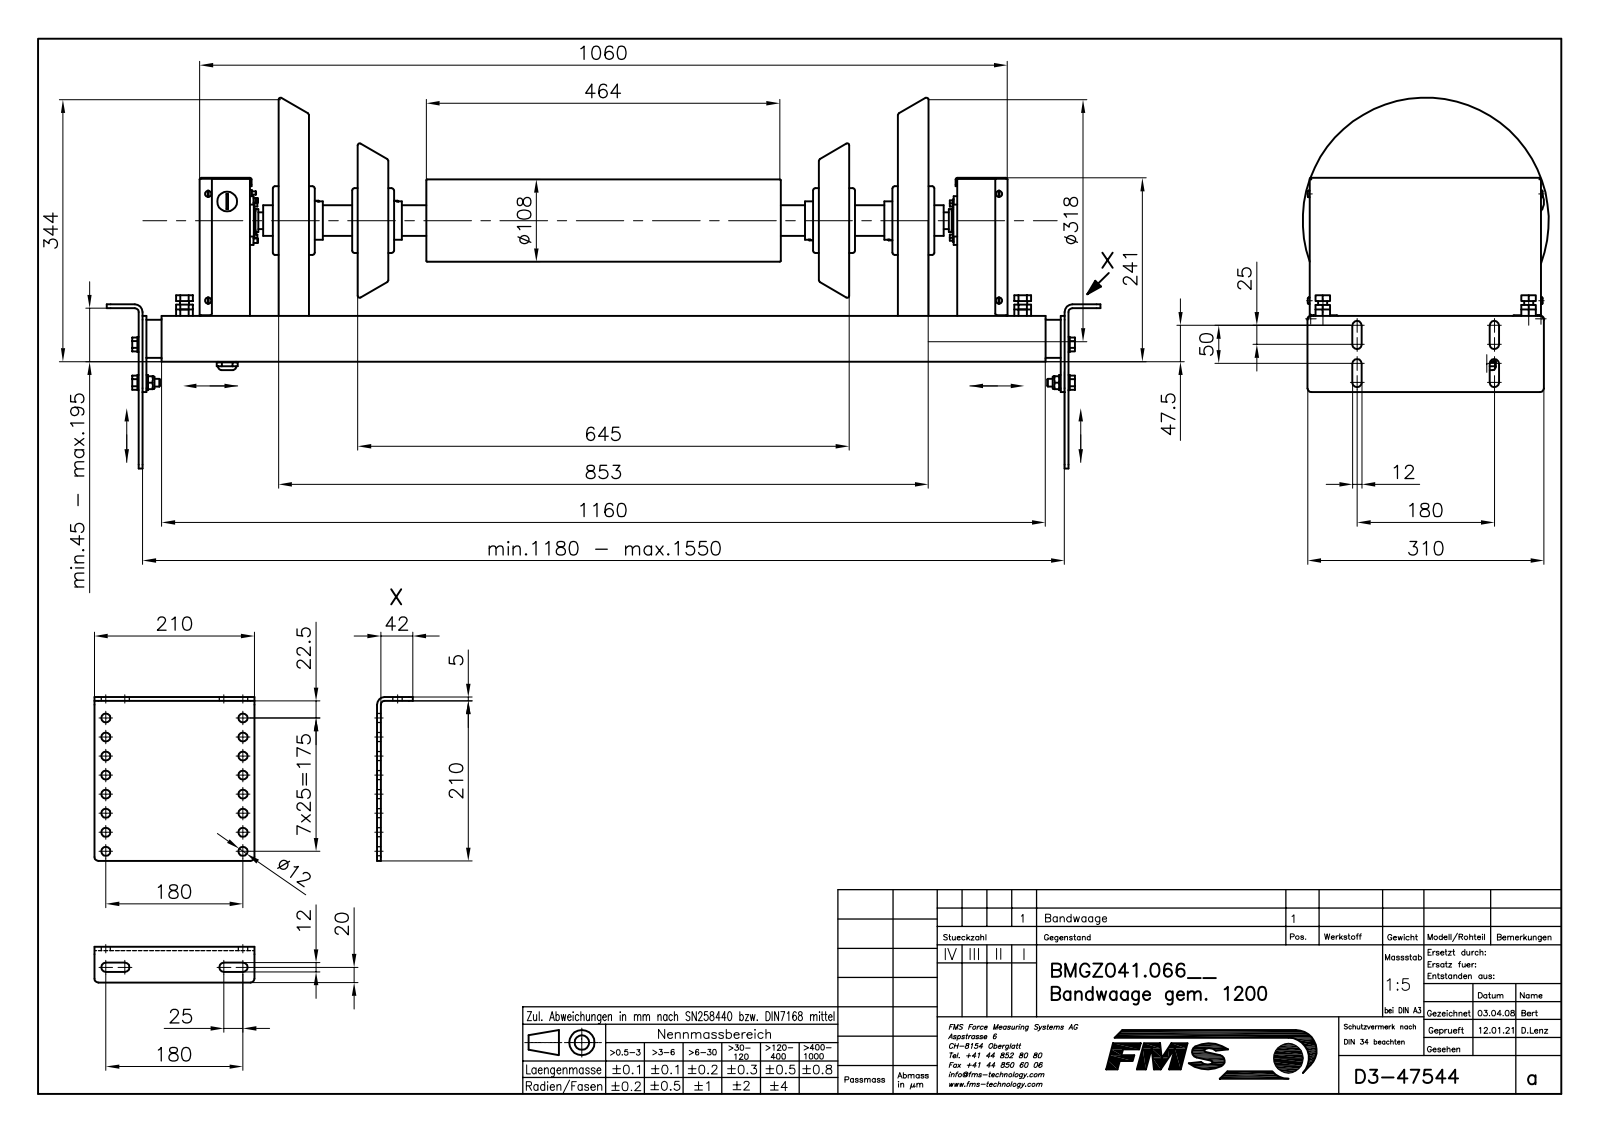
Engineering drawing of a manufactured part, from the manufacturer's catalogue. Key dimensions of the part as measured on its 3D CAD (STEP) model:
Part name (STEP PRODUCT): B47544_STP; B50109; 6KT-SCHRAUBE_M12X30; ZYL_SCHR__M4X8 (+8 more)
STEP written by: Mechanical Desktop 2009 (CONFIG_CONTROL_DESIGN)
Units: millimetres
Bodies: 179 solids, 2980 faces (1435 planar, 1070 cylindrical, 475 other)
Overall size (bounding box): 1304 × 486.26 × 322.53
Volume: 8 756 000 mm³ · Surface area: 4 035 000 mm²
Round holes (diameter × count): ⌀12 ×17, ⌀5 ×6, ⌀3.5 ×4, ⌀4.9 ×4, ⌀6.4 ×4, ⌀6.91 ×4, ⌀8.68 ×4, ⌀8.75 ×4, ⌀10 ×4, ⌀10.5 ×4, ⌀10.68 ×4, ⌀14.8 ×4
Round bosses / shafts (diameter × count): ⌀12 ×11, ⌀8.2 ×8, ⌀4.2 ×8, ⌀20 ×6, ⌀10 ×6, ⌀8 ×6, ⌀5 ×5, ⌀16 ×4
Partial cylindrical surfaces — rounded edges, fillets, slot ends (radius × count): R2 ×34, R1 ×24, R4 ×16, R5 ×16, R6 ×12, R3.5 ×8, R2.25 ×6, R0.5 ×4
Main face-to-face distances: 4, 5, 1, 270, 36, 3, 266, 32, 66, 65
Hole centre spacings: 25, 181.73, 50, 186.82, 75, 195, 100, 180
